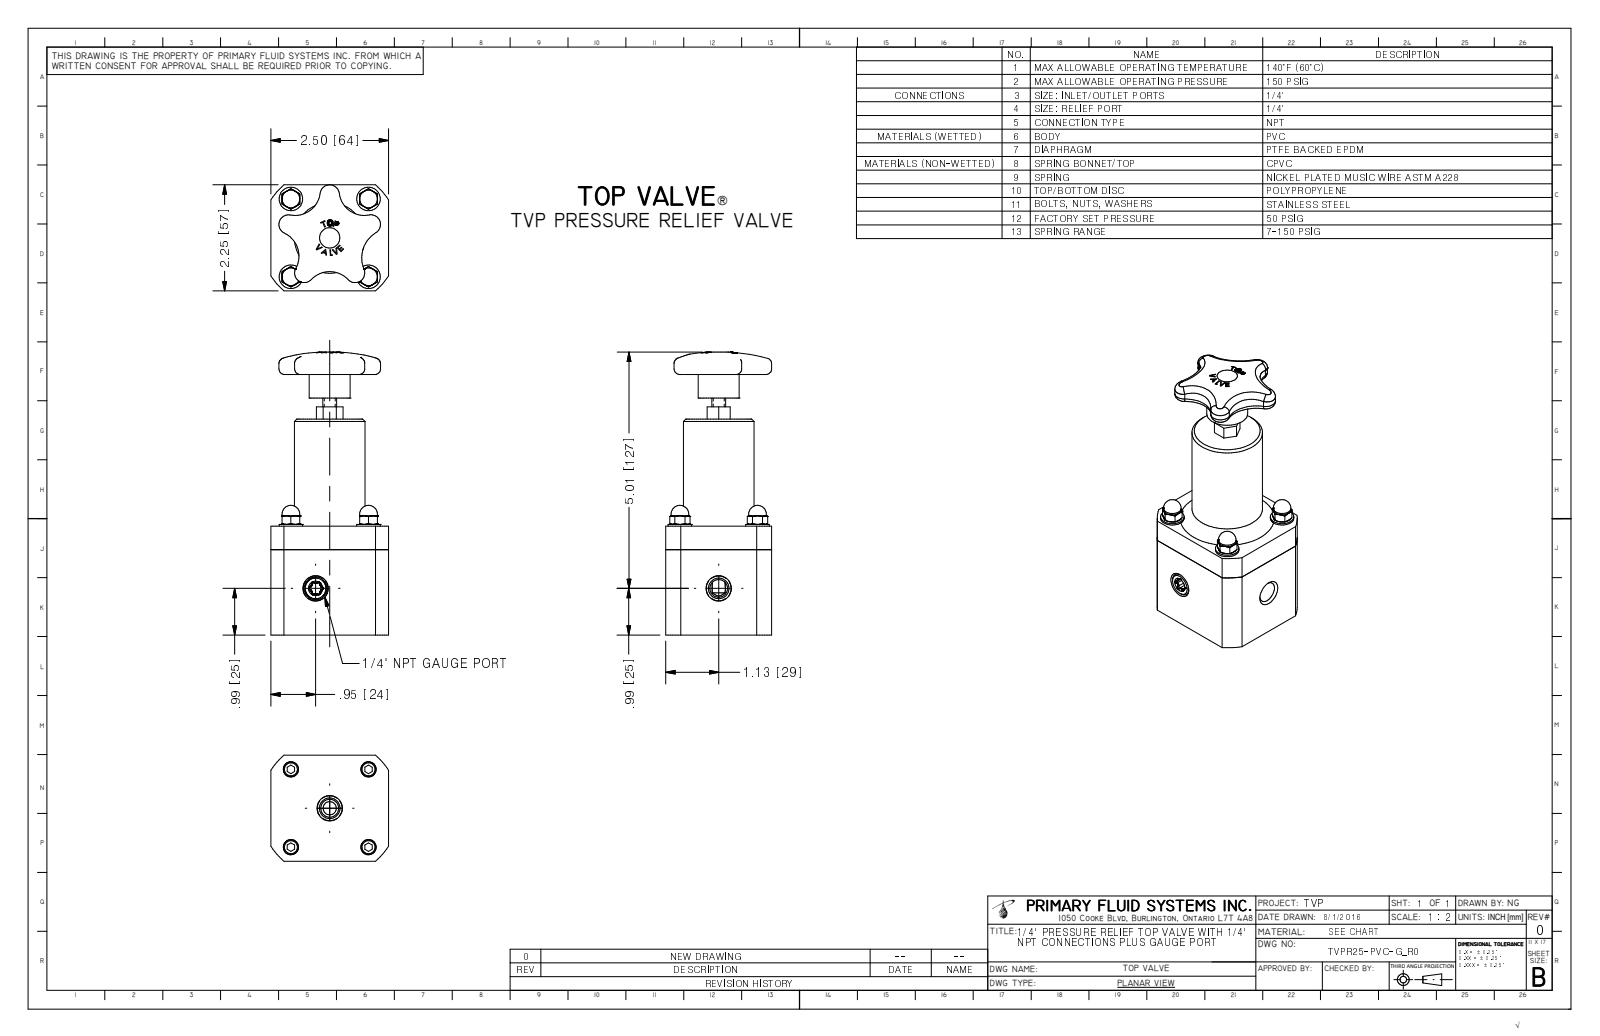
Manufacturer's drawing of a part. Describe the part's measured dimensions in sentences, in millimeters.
The part is named "TVPR25-PVC-G_R0". Its 3-D file was written by "Autodesk Inventor 2009 (AUTOMOTIVE_DESIGN)". It is 1 solid with 378 faces: 155 planar, 54 cylindrical and 169 other. Overall it measures 152.4 by 63.5 by 57.2 millimeters. Its volume is 291 000 cubic millimeters and its surface area 37 990 square millimeters. Round holes: 4 of diameter 3.7, 2 of diameter 11.1, 1 of diameter 38.7. Round bosses or shafts: 4 of diameter 12.7, 4 of diameter 9.5, 4 of diameter 7.9, 1 of diameter 38.1, 1 of diameter 22.1, 1 of diameter 7.4. Partial cylindrical surfaces (rounded edges, fillets, slot ends): 6 of radius 0.7, 5 of radius 2.2, 5 of radius 5.2, 4 of radius 13.6, 4 of radius 16.7, 1 of radius 15.9, 1 of radius 18.9, 1 of radius 37.8. The main face-to-face distances are 57.2, 63.5, 58.7, 116.3, 57.7, 127.7, 69, 11.3, 59.6, 0.9. The hole center spacings are 29.6, 29.6, 41.9, 41.9, 59.3.
